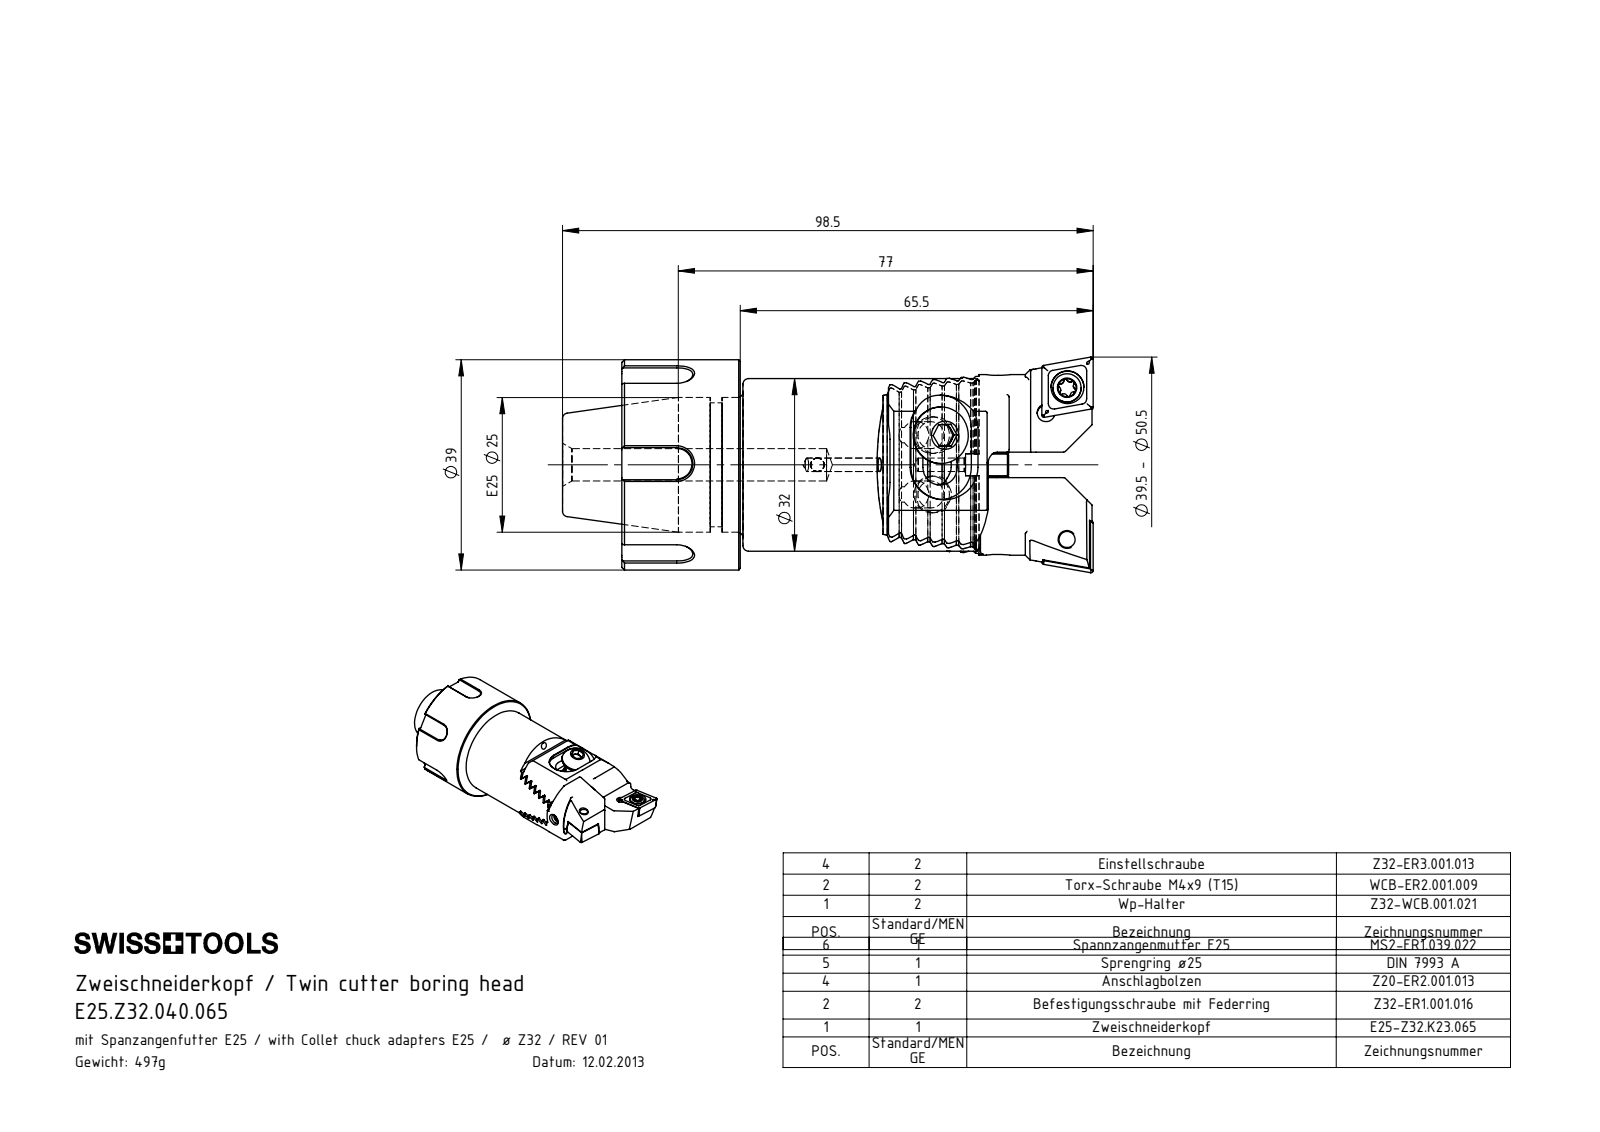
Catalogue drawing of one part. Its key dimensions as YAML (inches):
part_name: "Z32-ER1.002.016_A; MSX-ER1.XXX.XXX_A_Mutter Spannzangenkegel E25; Z20-ER2.001.013_A; E25-Z32.K23.065_B (+4 more)"
step_written_by: "SolidWorks 2017 (AUTOMOTIVE_DESIGN)"
units: inches
bodies: {solids: 8, faces: 317, planar: 177, cylindrical: 76, other: 64}
overall_size: [3.26, 1.535, 1.535]
volume: 3.142
surface_area: 28.59
round_holes:
  - {diameter: 0.098, count: 4}
  - {diameter: 0.197, count: 2}
  - {diameter: 0.252, count: 2}
  - {diameter: 0.268, count: 2}
  - {diameter: 0.079, count: 1}
  - {diameter: 0.236, count: 1}
  - {diameter: 1, count: 1}
  - {diameter: 1.157, count: 1}
  - {diameter: 1.201, count: 1}
  - {diameter: 1.299, count: 1}
round_bosses_or_shafts:
  - {diameter: 0.413, count: 2}
  - {diameter: 0.402, count: 2}
  - {diameter: 0.236, count: 2}
  - {diameter: 1.535, count: 1}
  - {diameter: 1.26, count: 1}
  - {diameter: 0.984, count: 1}
  - {diameter: 0.906, count: 1}
  - {diameter: 0.157, count: 1}
partial_cylinders:
  - {radius: 0.008, count: 14}
  - {radius: 0.012, count: 12}
  - {radius: 8.661, count: 2}
face_to_face_distances: [0.094, 0.187, 0.281, 0.375, 0.866, 0.732, 0.134, 0.646, 0.087, 0.22]
